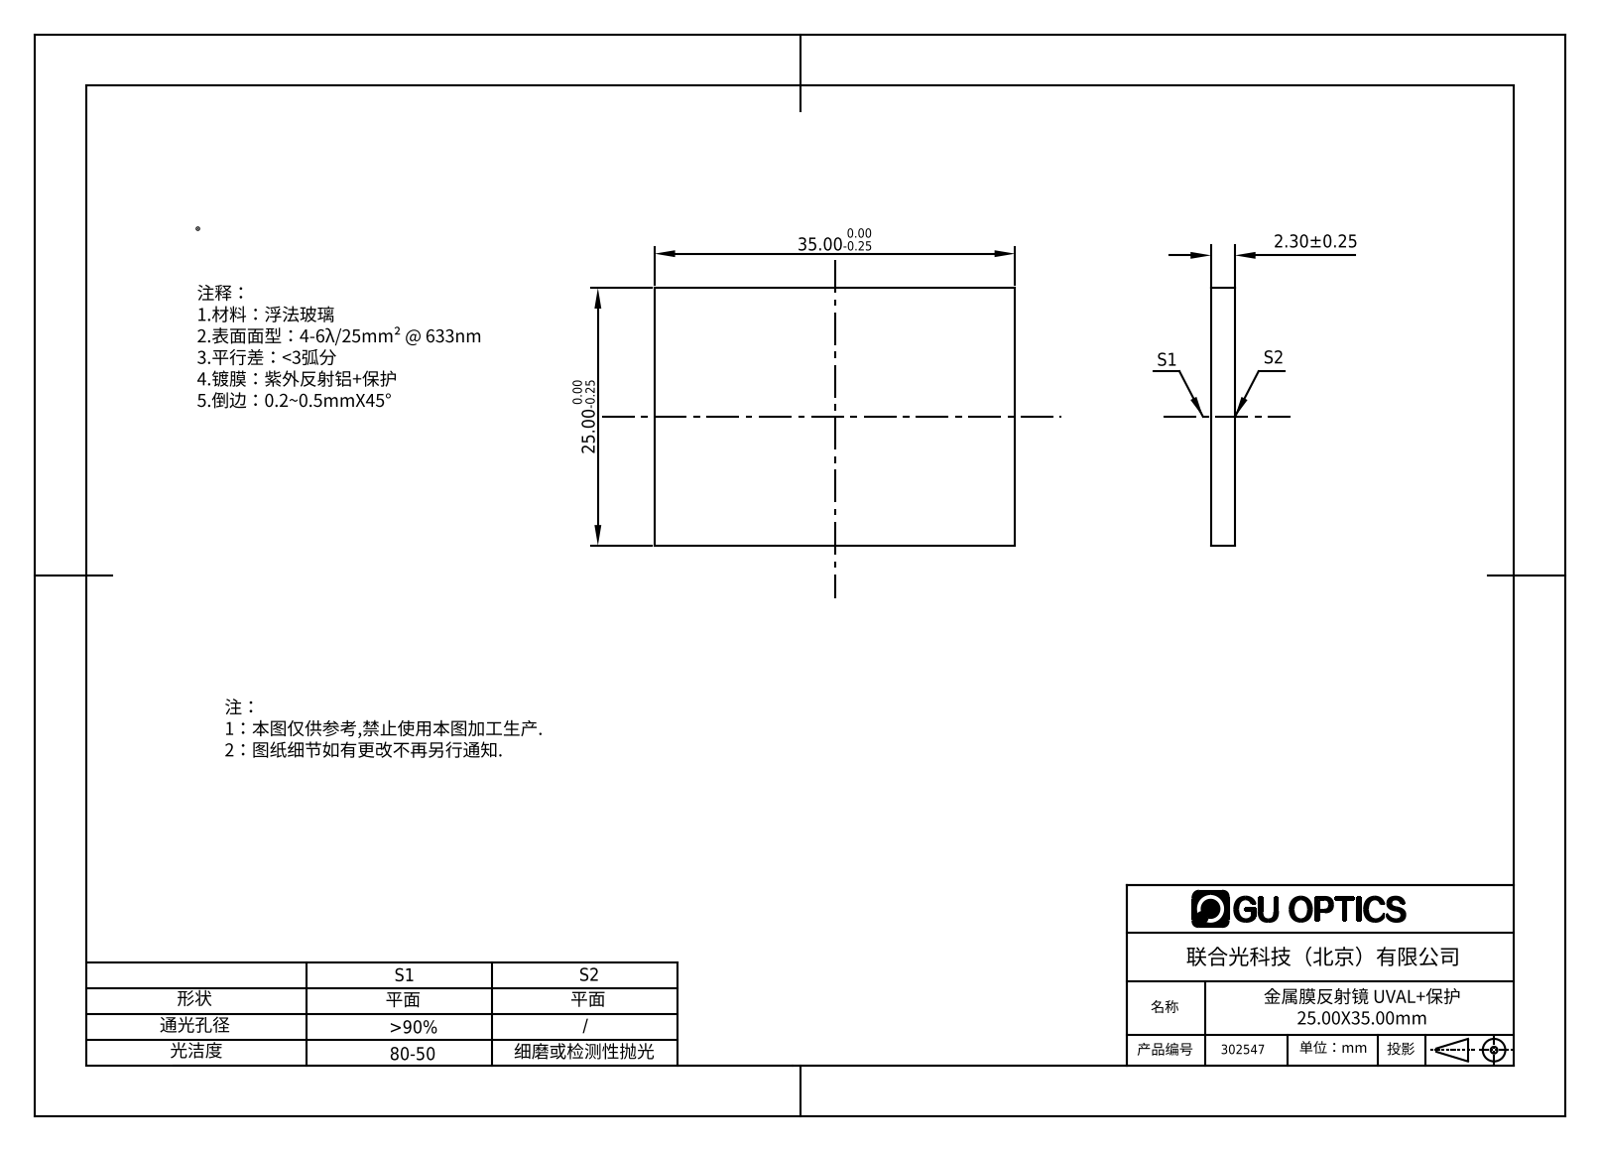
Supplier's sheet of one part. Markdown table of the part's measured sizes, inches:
| quantity | value |
| --- | --- |
| part name | 302518 |
| STEP written by | SolidWorks 2016 (AUTOMOTIVE_DESIGN) |
| units | inches |
| bodies | 1 solid, 6 faces (6 planar, 0 cylindrical, 0 other) |
| overall size | 1.378 × 0.984 × 0.091 |
| volume | 0.123 in³ |
| surface area | 3.14 in² |
| main face-to-face distances | 0.091, 0.984, 1.378 |
